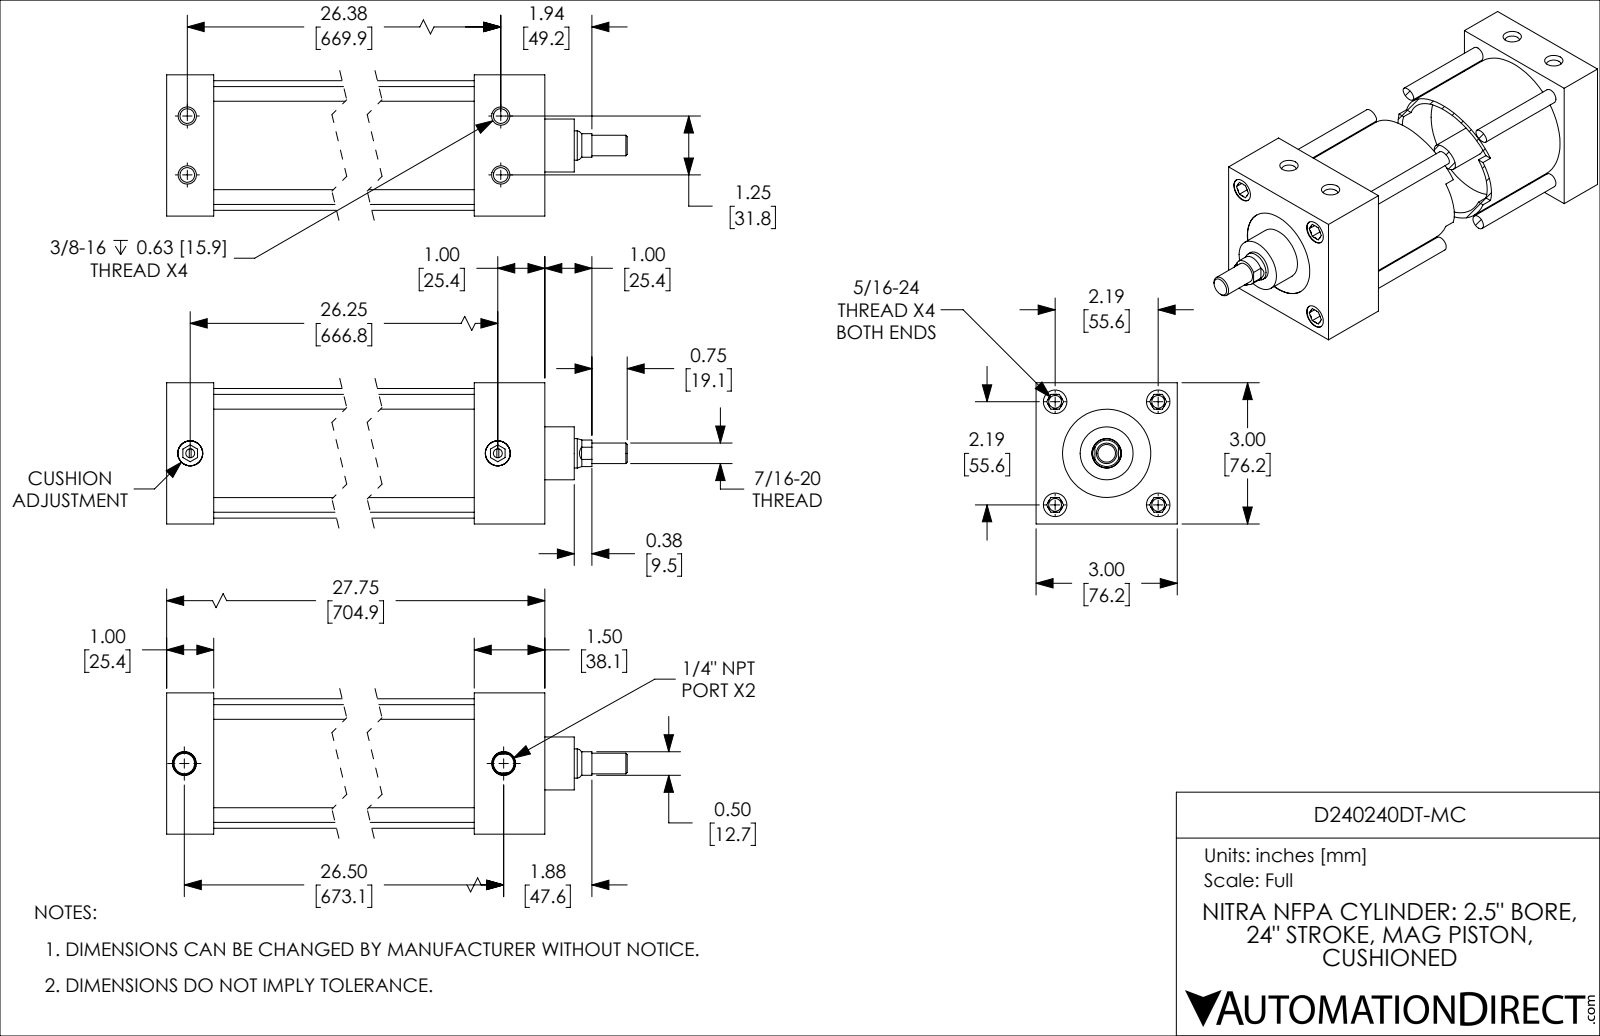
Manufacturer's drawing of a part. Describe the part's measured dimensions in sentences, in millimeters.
The part is named "D240240DT-MC_PISTON_KK1; D240240DT-MC_CUSHION; D240240DT-MC; D240240DT-MC_BODY". Its 3-D file was written by "SolidWorks 2019 (CONFIG_CONTROL_DESIGN)". It is 4 solids with 248 faces: 90 planar, 78 cylindrical and 80 other. Overall it measures 749.3 by 76.2 by 76.2 millimeters. Its volume is 1 138 000 cubic millimeters and its surface area 433 200 square millimeters. Round holes: 4 of diameter 6.9, 4 of diameter 8, 4 of diameter 12.7, 2 of diameter 4.8, 2 of diameter 11.1, 2 of diameter 13.5, 1 of diameter 15.9, 1 of diameter 47.6, 1 of diameter 63.5. Round bosses or shafts: 4 of diameter 7.9, 2 of diameter 13.5, 1 of diameter 69.9, 1 of diameter 63.5, 1 of diameter 28.6, 1 of diameter 15.8, 1 of diameter 11.1. Partial cylindrical surfaces (rounded edges, fillets, slot ends): 1 of radius 7.1. The main face-to-face distances are 76.2, 25.4, 666.8, 641.4, 704.9, 679.5, 38.1, 31.8, 57.2, 609.6. The hole center spacings are 39.3, 55.6, 671.7, 16, 16, 31.8, 78.7, 669.9.
